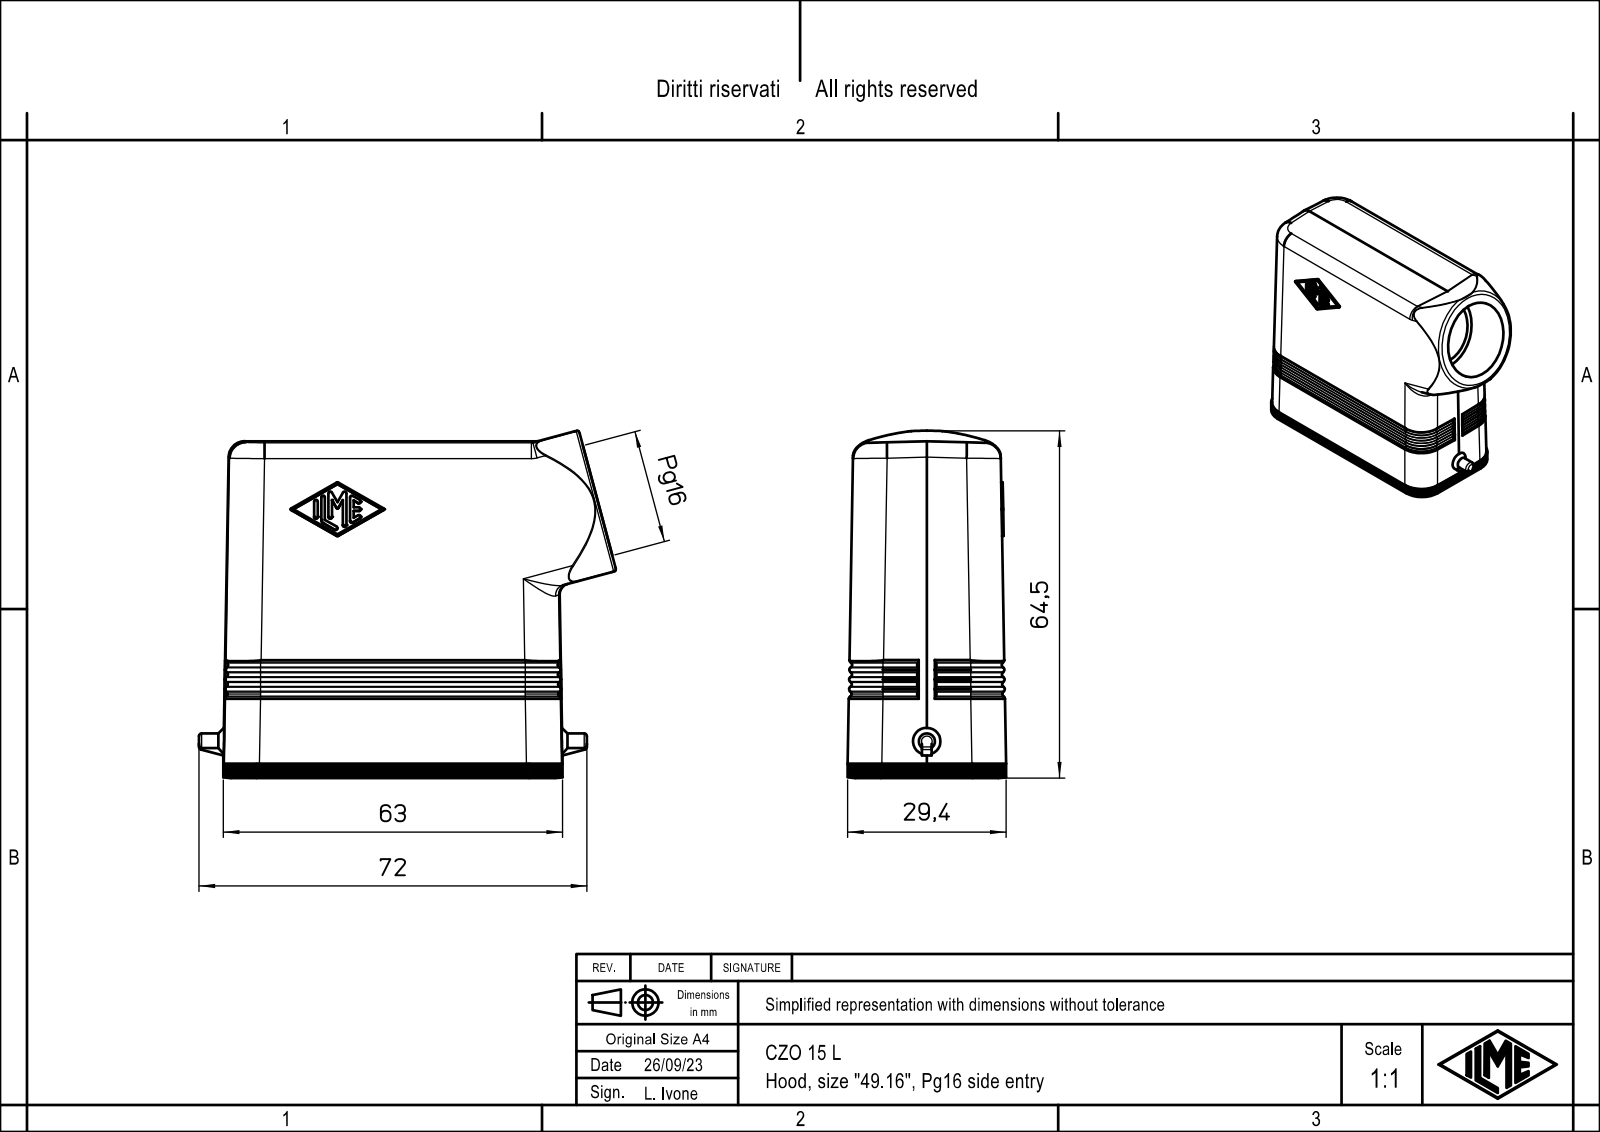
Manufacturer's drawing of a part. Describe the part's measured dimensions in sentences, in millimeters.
The part is named "CZO 15 L". Its 3-D file was written by "Creo Elements/Direct Modeling 20.1B 02-Apr-2019 (C) Parametric Technology GmbH (AUTOMOTIVE_DESIGN)". It is 1 solid with 450 faces: 165 planar, 131 cylindrical and 154 other. Overall it measures 77.38 by 64.45 by 29.4 millimeters. Its volume is 35 178 cubic millimeters and its surface area 24 703 square millimeters. Round holes: 4 of diameter 2.75, 1 of diameter 18, 1 of diameter 21.1. Round bosses or shafts: 1 of diameter 3. Partial cylindrical surfaces (rounded edges, fillets, slot ends): 56 of radius 0.5, 11 of radius 2, 10 of radius 1.5, 6 of radius 3, 4 of radius 3.3, 4 of radius 3.5, 4 of radius 6, 4 of radius 6.2. The main face-to-face distances are 24.3, 7.15, 50.65, 7.05, 17.25, 2.9, 57.8, 2.55, 9.6, 19.8. The hole center spacings are 16, 49.5, 52.02.
